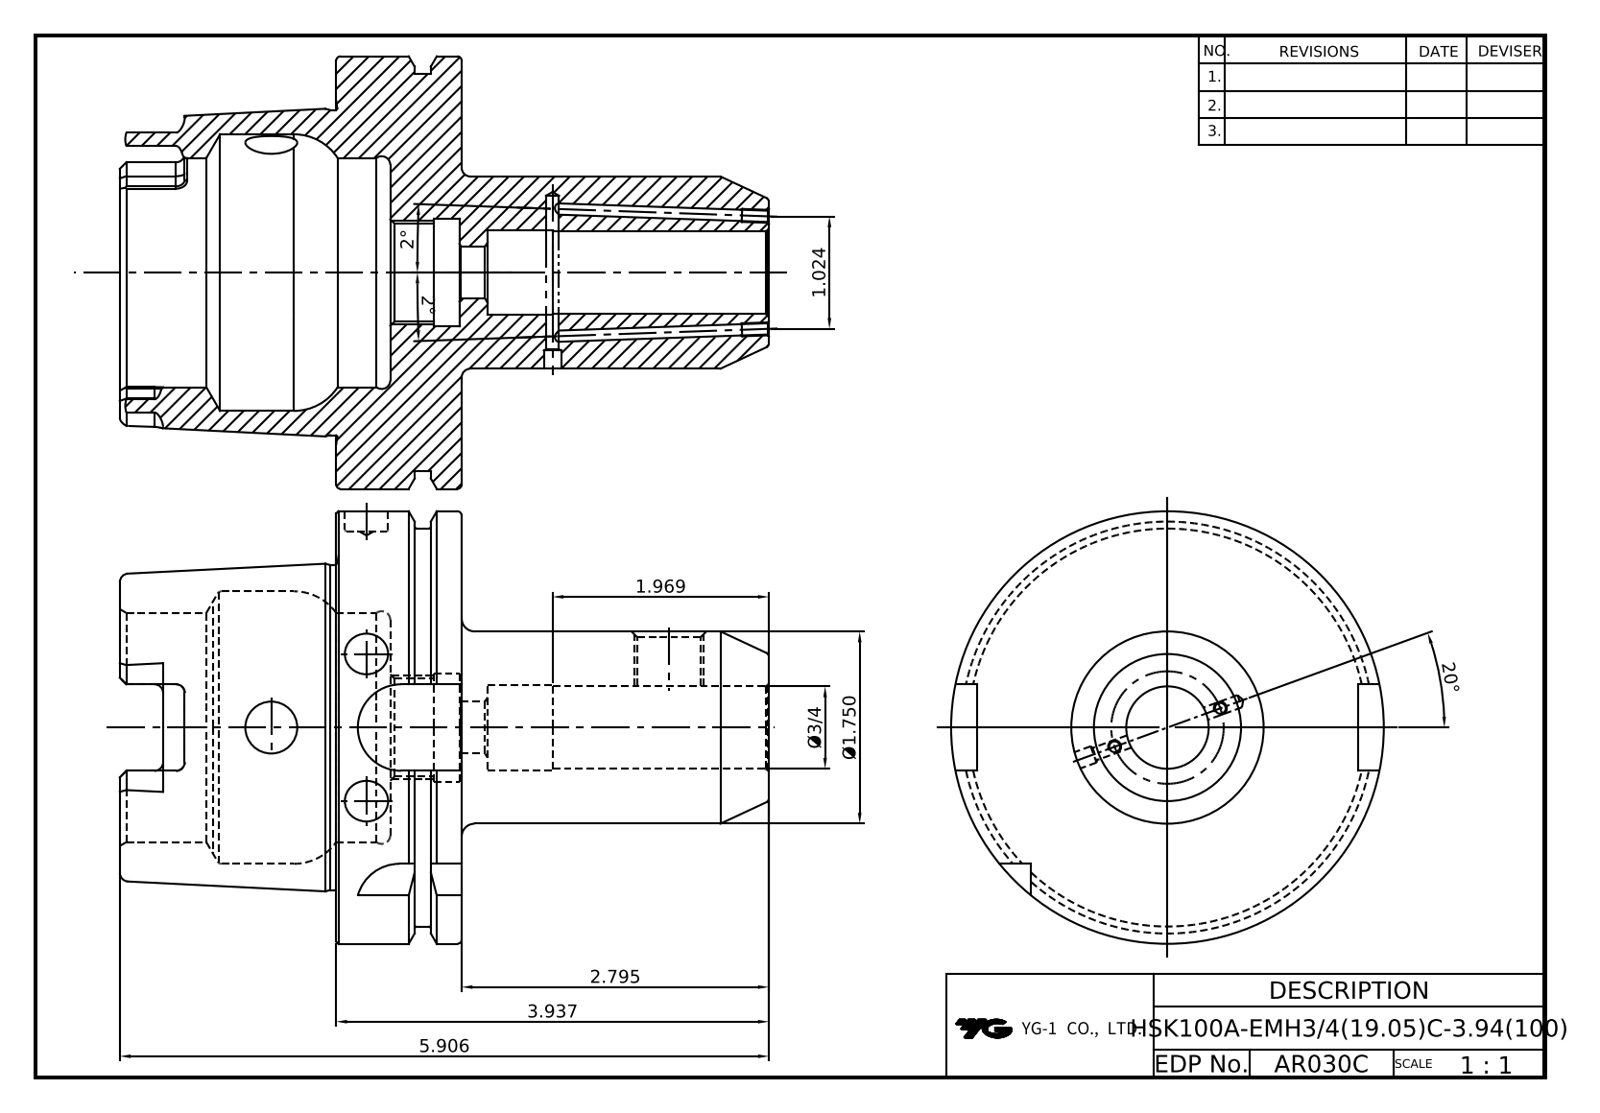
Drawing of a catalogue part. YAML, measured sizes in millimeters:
part_name: "LO-HSK100A-EMH19.05C-100"
step_written_by: "Autodesk Inventor 2020 (AUTOMOTIVE_DESIGN)"
units: millimeters
bodies: {solids: 1, faces: 134, planar: 42, cylindrical: 42, other: 50}
overall_size: [150, 100, 100]
volume: 337097
surface_area: 64126
round_holes:
  - {diameter: 10, count: 3}
  - {diameter: 2.46, count: 2}
  - {diameter: 12, count: 2}
  - {diameter: 3, count: 1}
  - {diameter: 4, count: 1}
  - {diameter: 14.35, count: 1}
  - {diameter: 19.05, count: 1}
  - {diameter: 20.25, count: 1}
  - {diameter: 22.38, count: 1}
  - {diameter: 25, count: 1}
  - {diameter: 53, count: 1}
  - {diameter: 63, count: 1}
round_bosses_or_shafts:
  - {diameter: 100, count: 1}
  - {diameter: 92, count: 1}
  - {diameter: 75.41, count: 1}
  - {diameter: 44.45, count: 1}
partial_cylinders:
  - {radius: 2, count: 6}
  - {radius: 4.88, count: 4}
  - {radius: 10, count: 4}
face_to_face_distances: [29, 12.5, 16.5, 62.5, 50, 79, 100, 150, 87.5, 71]
hole_center_spacings: [43, 69.9]
